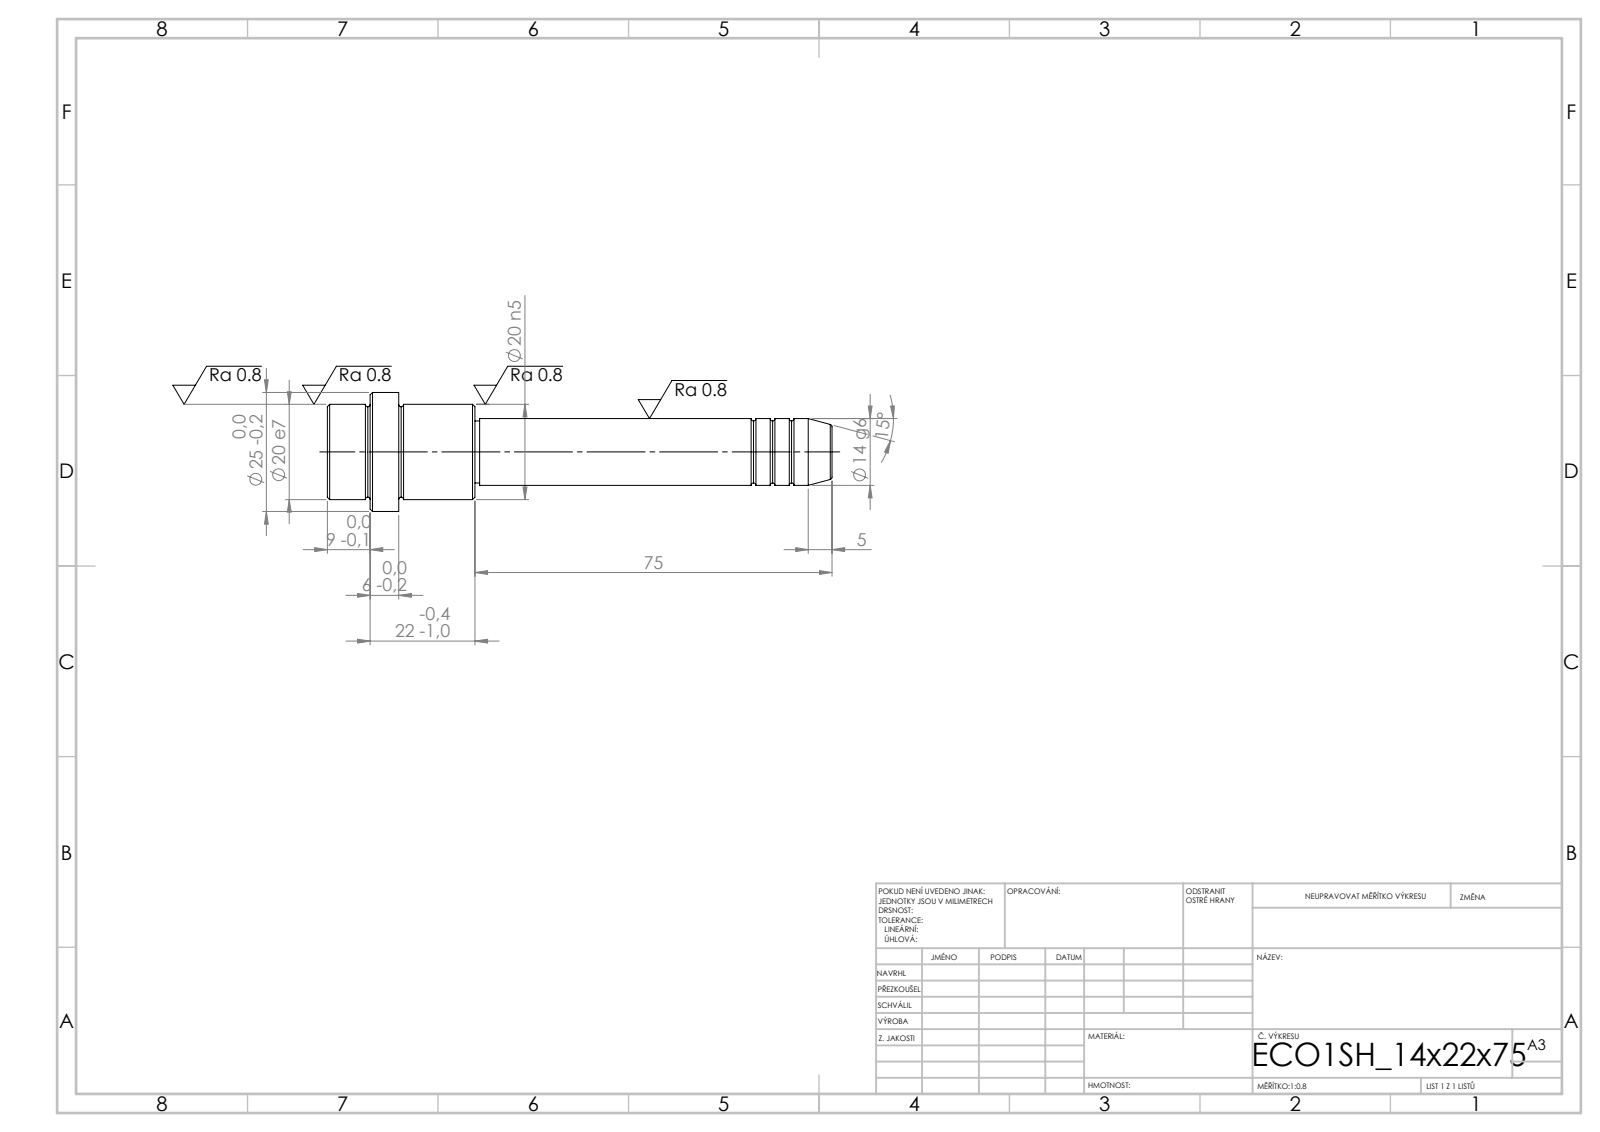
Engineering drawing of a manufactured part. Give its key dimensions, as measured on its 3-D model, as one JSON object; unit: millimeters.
{"step_written_by": "SolidWorks 2019 (CONFIG_CONTROL_DESIGN)", "units": "millimeters", "bodies": {"solids": 1, "faces": 52, "planar": 6, "cylindrical": 16, "other": 30}, "overall_size": [106, 25, 25], "volume_mm3": 22061, "surface_area_mm2": 6361, "round_bosses_or_shafts": [[25, 1], [20, 1], [14, 1], [13, 1]], "face_to_face_distances": [15, 16, 31, 22, 6, 9, 75, 91, 97, 106]}
